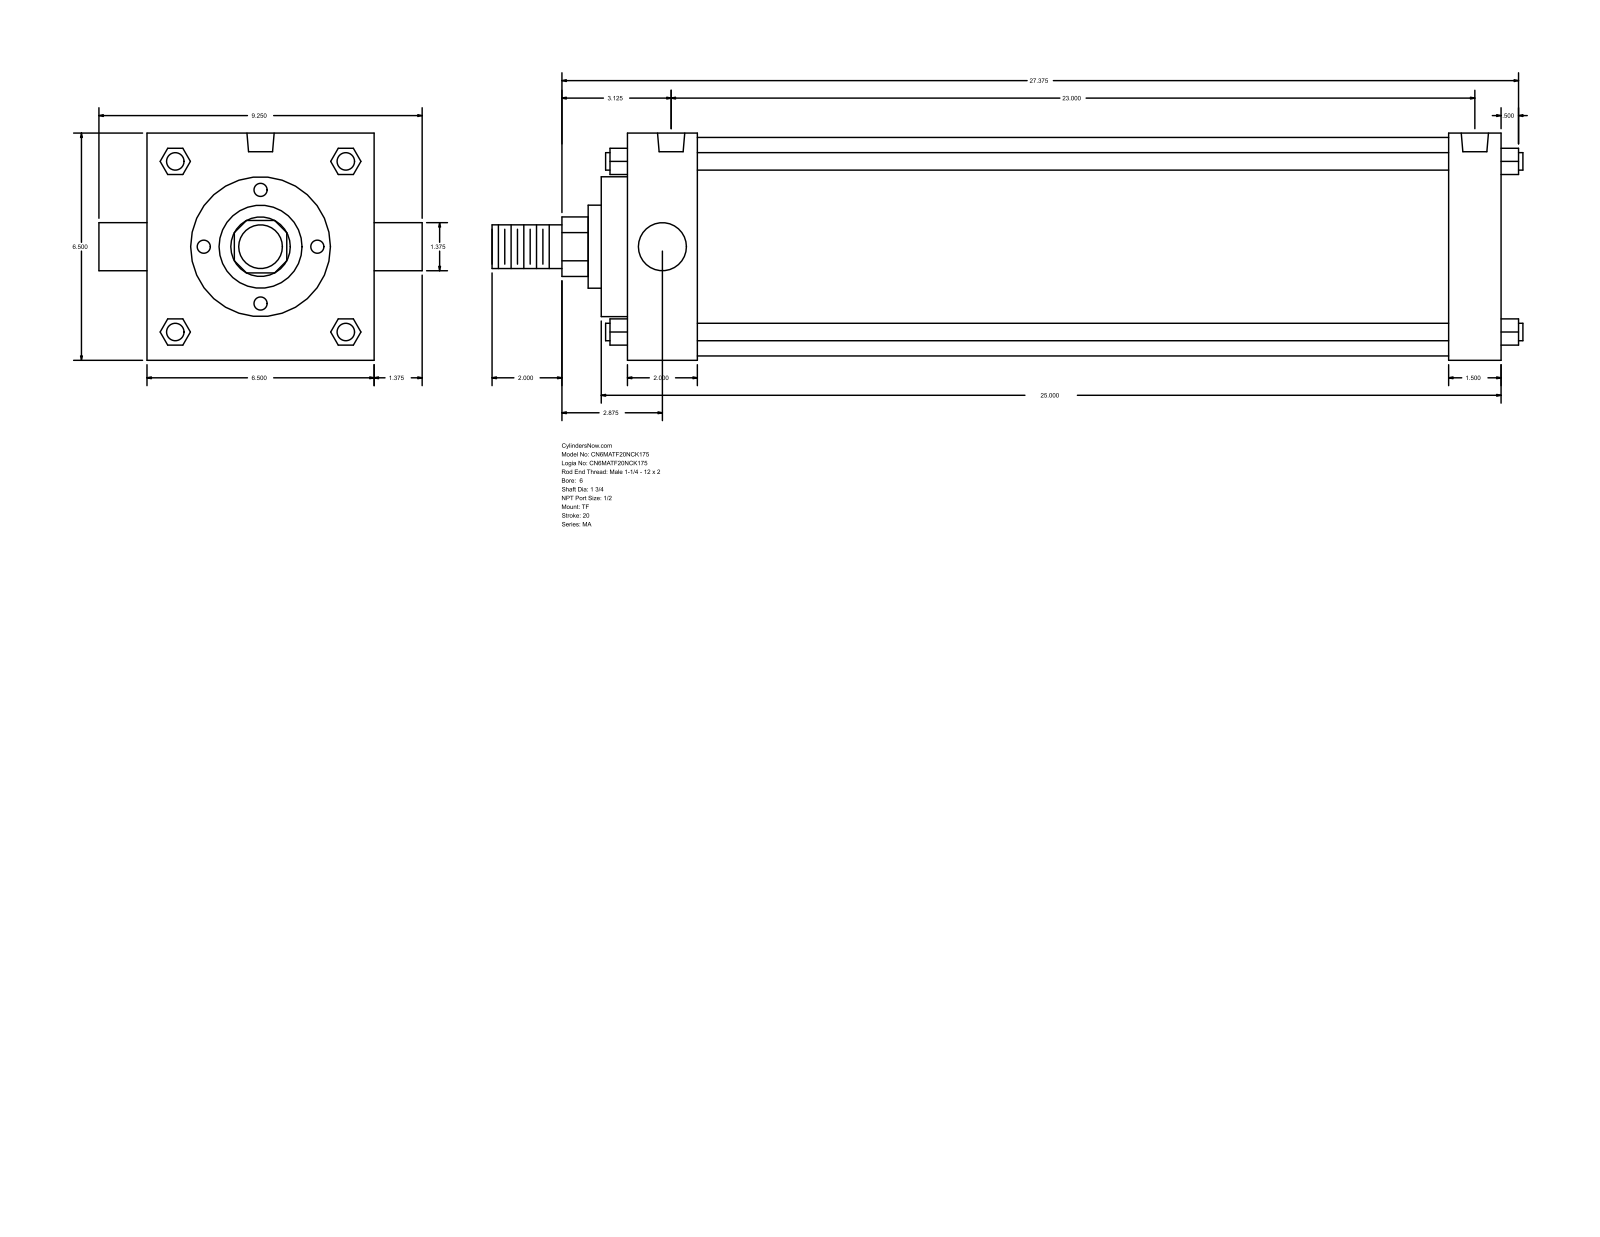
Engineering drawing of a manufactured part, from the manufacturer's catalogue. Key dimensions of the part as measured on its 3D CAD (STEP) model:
Part name (STEP PRODUCT): MA_TF__0600_1.75
STEP written by: GSSL Pune (CONFIG_CONTROL_DESIGN)
Units: millimetres
Bodies: 0 solids, 122 faces (93 planar, 29 cylindrical, 0 other)
Overall size (bounding box): 749.3 × 234.95 × 165.1
Round holes (diameter × count): ⌀17.46 ×3, ⌀19.77 ×2
Round bosses / shafts (diameter × count): ⌀12.7 ×4, ⌀158.75 ×1, ⌀101.6 ×1, ⌀60.33 ×1, ⌀44.45 ×1, ⌀34.92 ×1, ⌀31.75 ×1
Partial cylindrical surfaces — rounded edges, fillets, slot ends (radius × count): R21.63 ×1
Main face-to-face distances: 165.1, 635, 19.05, 38.1, 50.8, 584.2, 596.9, 546.1, 69.85, 615.95
Hole centre spacings: 584.2
